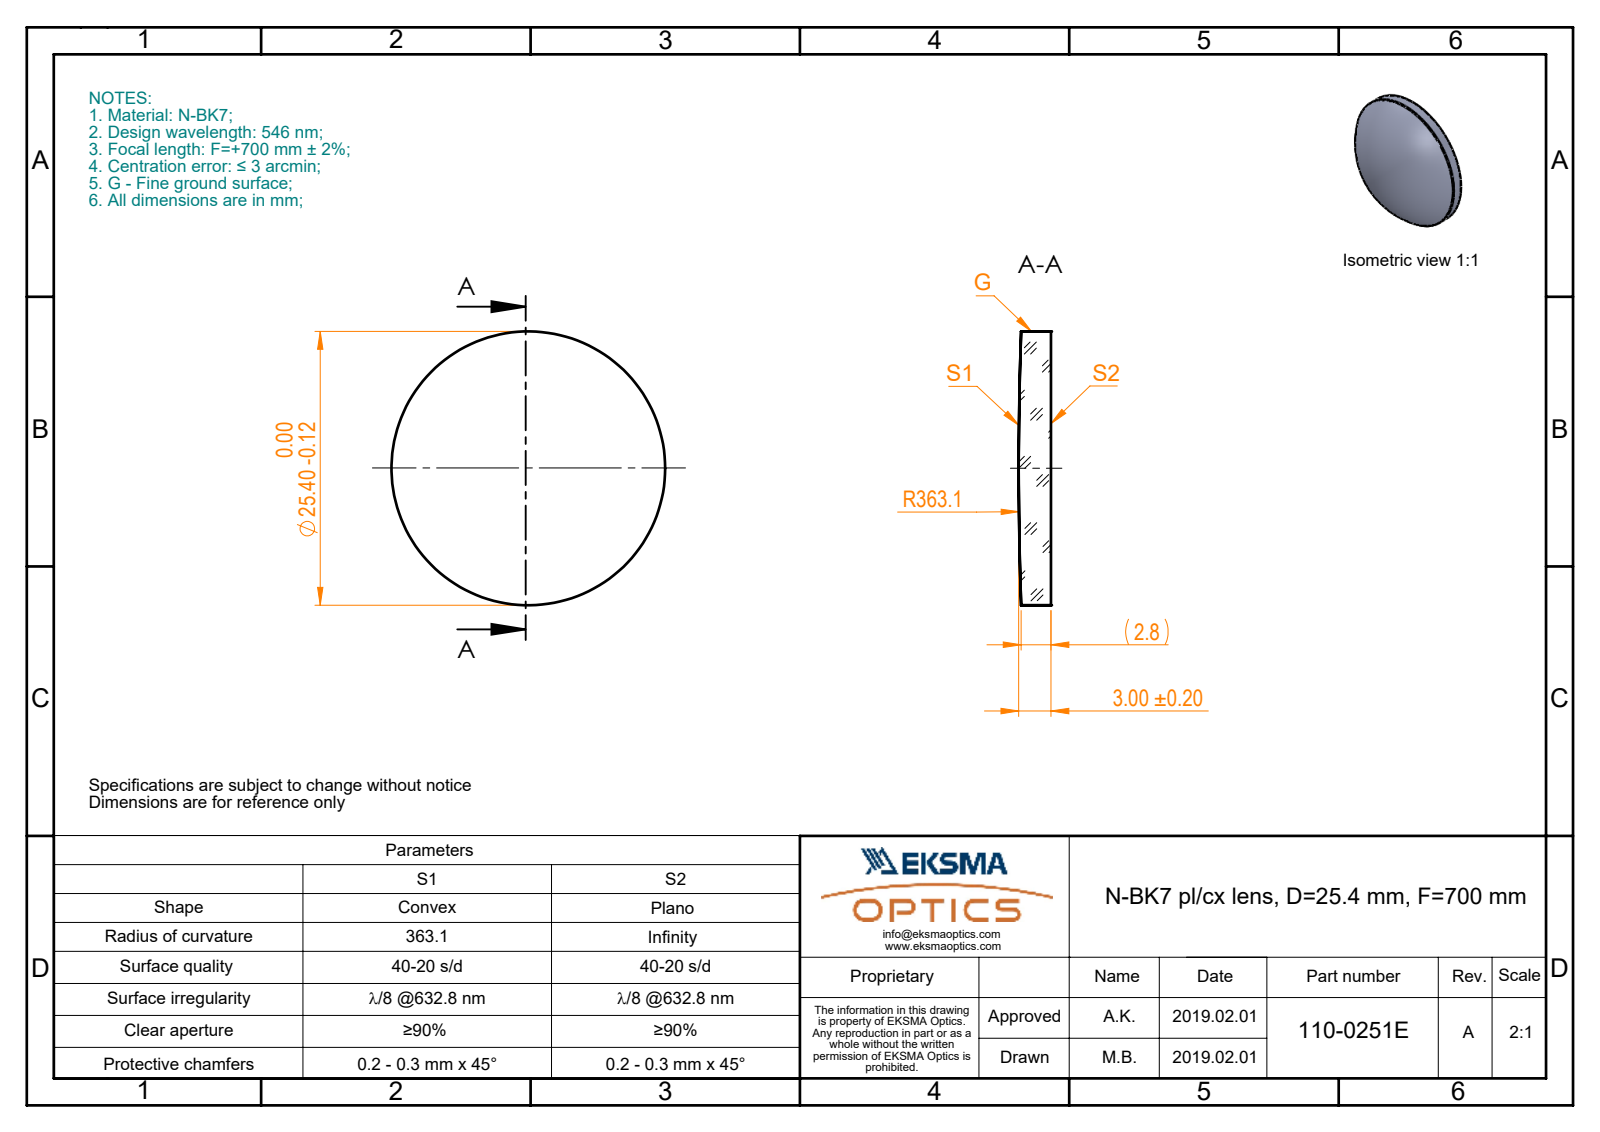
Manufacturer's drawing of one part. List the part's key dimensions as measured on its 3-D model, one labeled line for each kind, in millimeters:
Part name (STEP PRODUCT): 110-0251E BK7 pl-cx 25.4 F700
STEP written by: SolidWorks 2017 (CONFIG_CONTROL_DESIGN)
Units: millimetres
Bodies: 1 solid, 5 faces (1 planar, 2 cylindrical, 2 other)
Overall size (bounding box): 25.4 × 25.4 × 3
Volume: 1 464 mm³ · Surface area: 1 235 mm²
Round bosses / shafts (diameter × count): ⌀25.4 ×1
